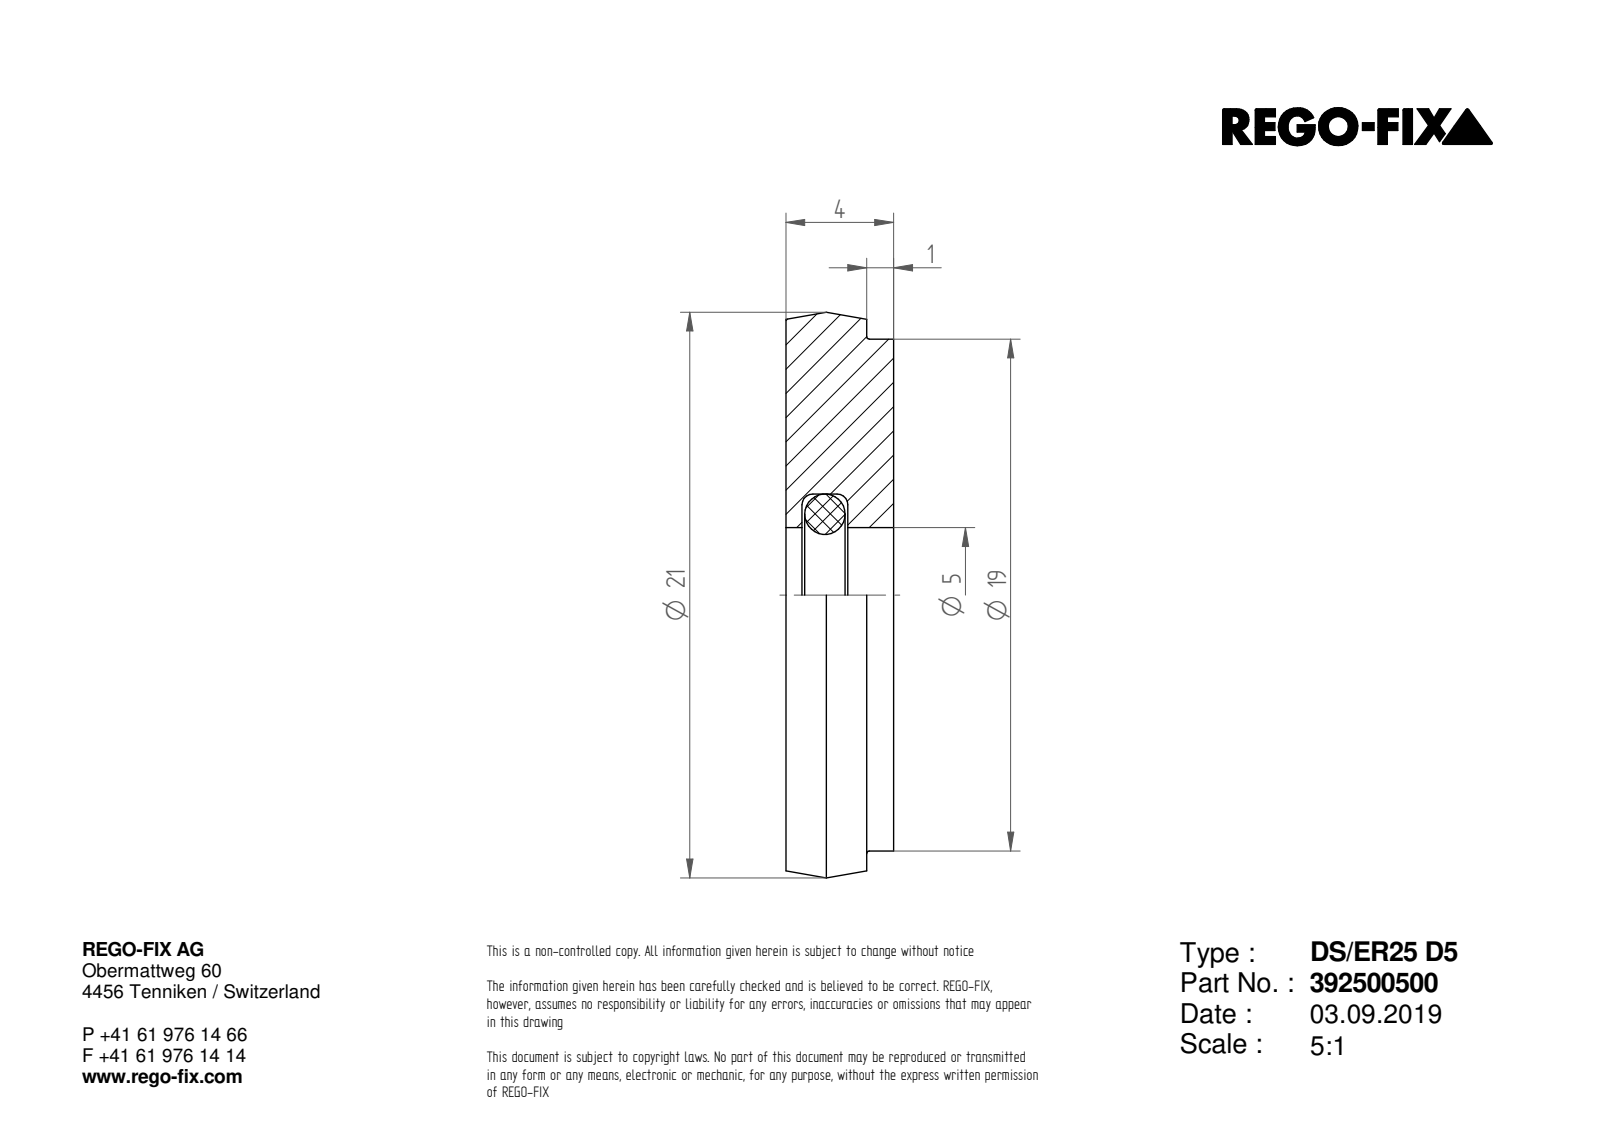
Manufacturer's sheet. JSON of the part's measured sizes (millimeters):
{"part_name": "NOCUT", "step_written_by": "SIEMENS PLM Software Solid Edge ST10 (AUTOMOTIVE_DESIGN)", "units": "millimeters", "bodies": {"solids": 1, "faces": 7, "planar": 3, "cylindrical": 3, "other": 1}, "overall_size": [21, 21, 4], "volume_mm3": 1244, "surface_area_mm2": 971, "round_holes": [[5, 1]], "round_bosses_or_shafts": [[21, 1], [19, 1]], "face_to_face_distances": [4, 1, 3]}
